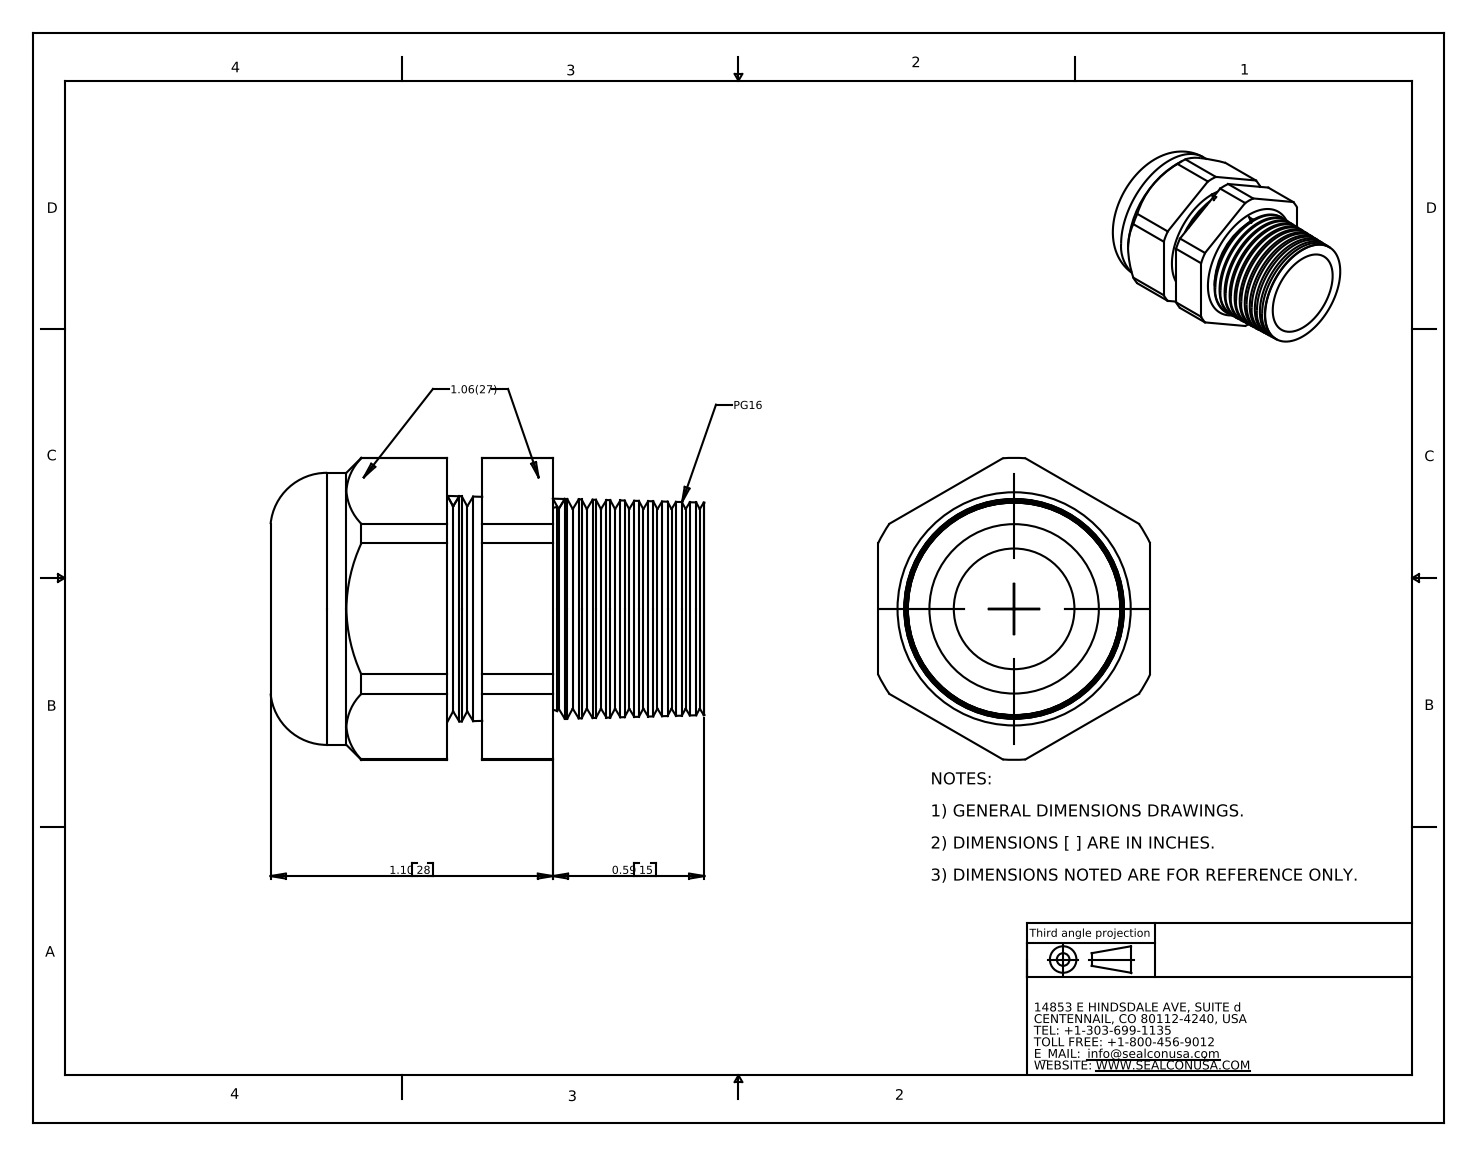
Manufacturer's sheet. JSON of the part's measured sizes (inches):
{"part_name": "CD16CR-BK", "step_written_by": "SolidWorks 2007 (CONFIG_CONTROL_DESIGN)", "units": "inches", "bodies": {"solids": 2, "faces": 135, "planar": 19, "cylindrical": 22, "other": 94}, "overall_size": [1.69, 1.177, 1.06], "volume_in3": 0.881, "surface_area_in2": 12.66, "round_holes": [[0.47, 1], [0.66, 1]], "round_bosses_or_shafts": [[1.06, 1]], "partial_cylinders_radius": [[0.588, 1]], "face_to_face_distances": [1.06, 0.135, 0.394, 0.529, 0.805, 0.411, 0.276, 1.394, 1.001, 0.865]}
